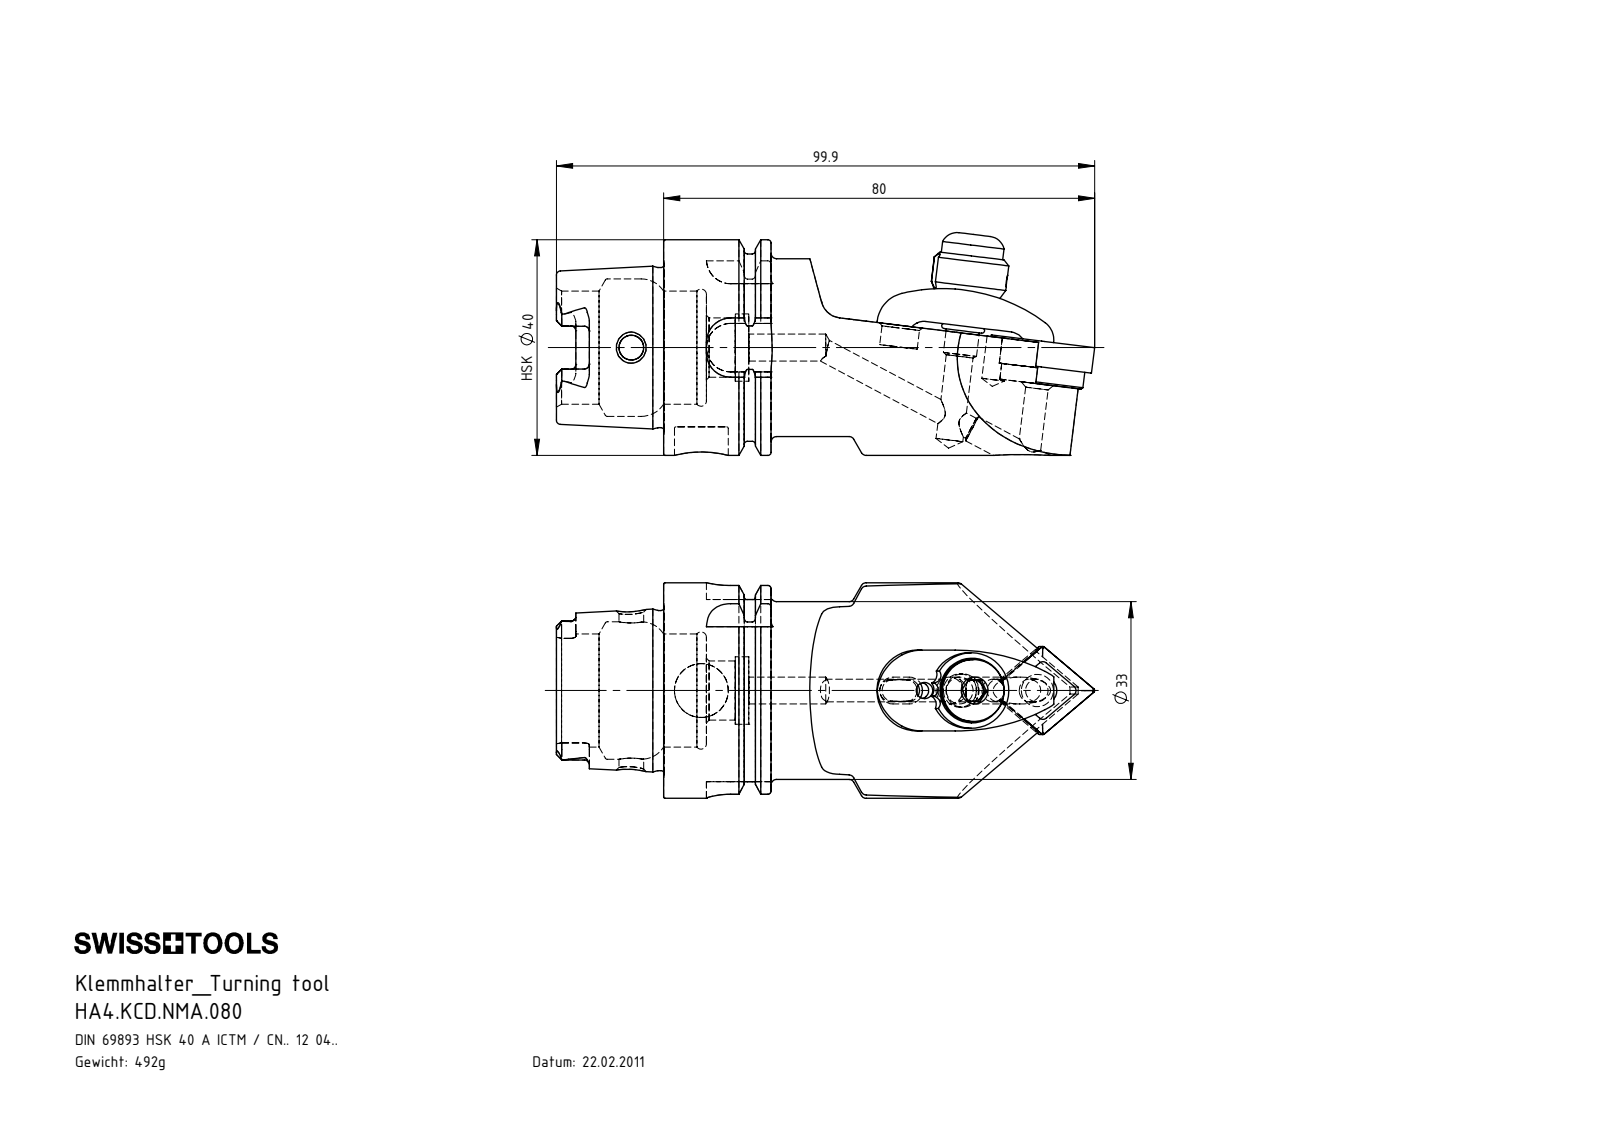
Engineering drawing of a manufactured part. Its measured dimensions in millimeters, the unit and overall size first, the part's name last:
Units: millimetres
Overall size (bounding box): 99.9 × 41.35 × 40
Round holes (diameter × count): ⌀2 ×3, ⌀4.2 ×3, ⌀5 ×3, ⌀7 ×2, ⌀3 ×1, ⌀4 ×1, ⌀4.6 ×1, ⌀5.16 ×1, ⌀6.2 ×1, ⌀6.4 ×1, ⌀8.5 ×1, ⌀10 ×1
Round bosses / shafts (diameter × count): ⌀6.2 ×2, ⌀5 ×2, ⌀40 ×1, ⌀34.75 ×1, ⌀33 ×1, ⌀29.71 ×1, ⌀14 ×1, ⌀11.5 ×1
Partial cylindrical surfaces — rounded edges, fillets, slot ends (radius × count): R0.39 ×6, R0.9 ×6, R0.4 ×4, R1 ×4, R1.88 ×4, R4.5 ×4, R0.69 ×3, R0.69 ×3
Main face-to-face distances: 7.64, 3.18, 4.46, 7.95, 11.69, 1.3, 8.94, 5.76, 12, 19.95
Hole centre spacings: 6.48, 6.67, 6.68, 8, 8.01, 8.2, 8.26, 8.32
Volume: 64 641 mm³ · Surface area: 21 589 mm²
Bodies: 12 solids, 469 faces (129 planar, 154 cylindrical, 186 other)
Part name (STEP PRODUCT): HA4-KCD.NMA.080_A_Fertigbearbeitung; WCD-ER2.101.003_A; KVT_MB_600_050; WCC-ER3.102.024_C (+6 more)
STEP written by: SolidWorks 2017 (CONFIG_CONTROL_DESIGN)
